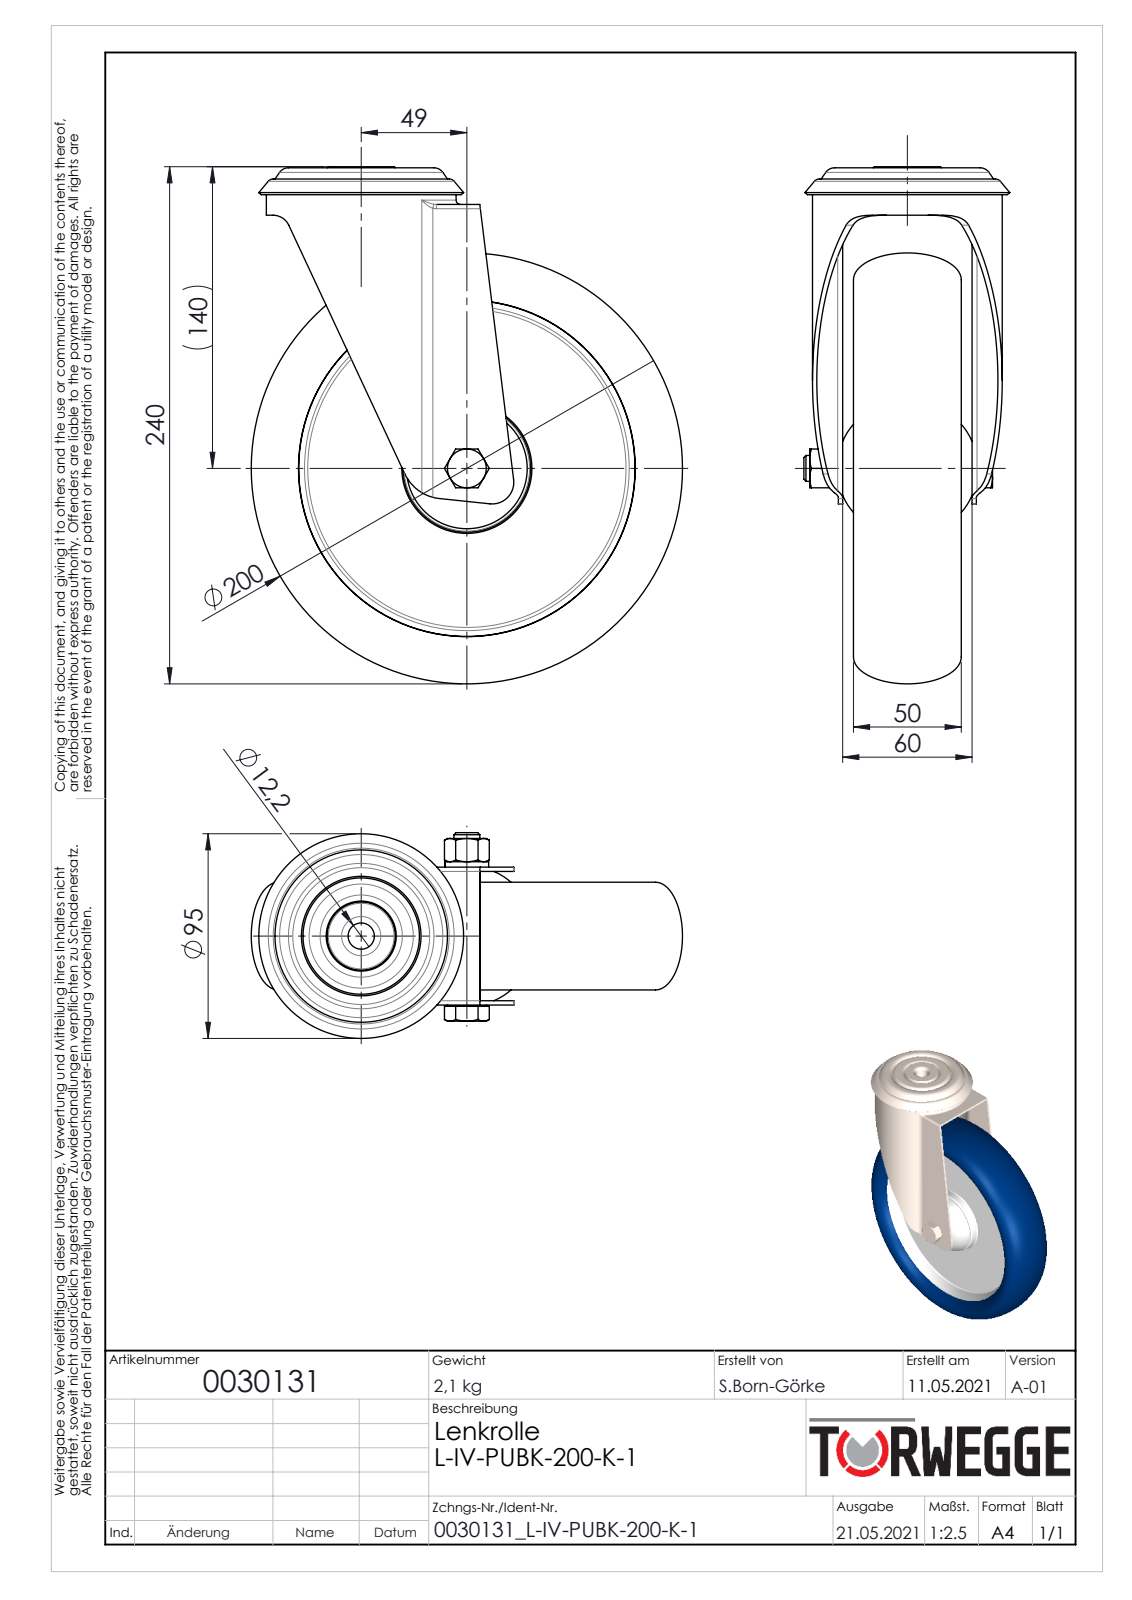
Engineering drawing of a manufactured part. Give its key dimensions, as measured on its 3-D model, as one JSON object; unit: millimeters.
{"part_name": "0030131", "step_written_by": "SolidWorks 2020 (AUTOMOTIVE_DESIGN)", "units": "millimeters", "bodies": {"solids": 8, "faces": 255, "planar": 63, "cylindrical": 54, "other": 138}, "overall_size": [240, 199.5, 95.5], "volume_mm3": 930290, "surface_area_mm2": 254142, "round_holes": [[12.2, 2], [10.2, 1], [12, 1], [12.3, 1], [44, 1], [47, 1], [84, 1]], "round_bosses_or_shafts": [[88, 1], [41, 1], [31.5, 1], [20.2, 1], [20, 1], [18, 1]], "partial_cylinders_radius": [[8, 3], [10, 3], [2, 2], [20, 1]], "face_to_face_distances": [11, 2, 26.5, 24.5, 35.5, 62, 37.5, 60, 64, 6]}
